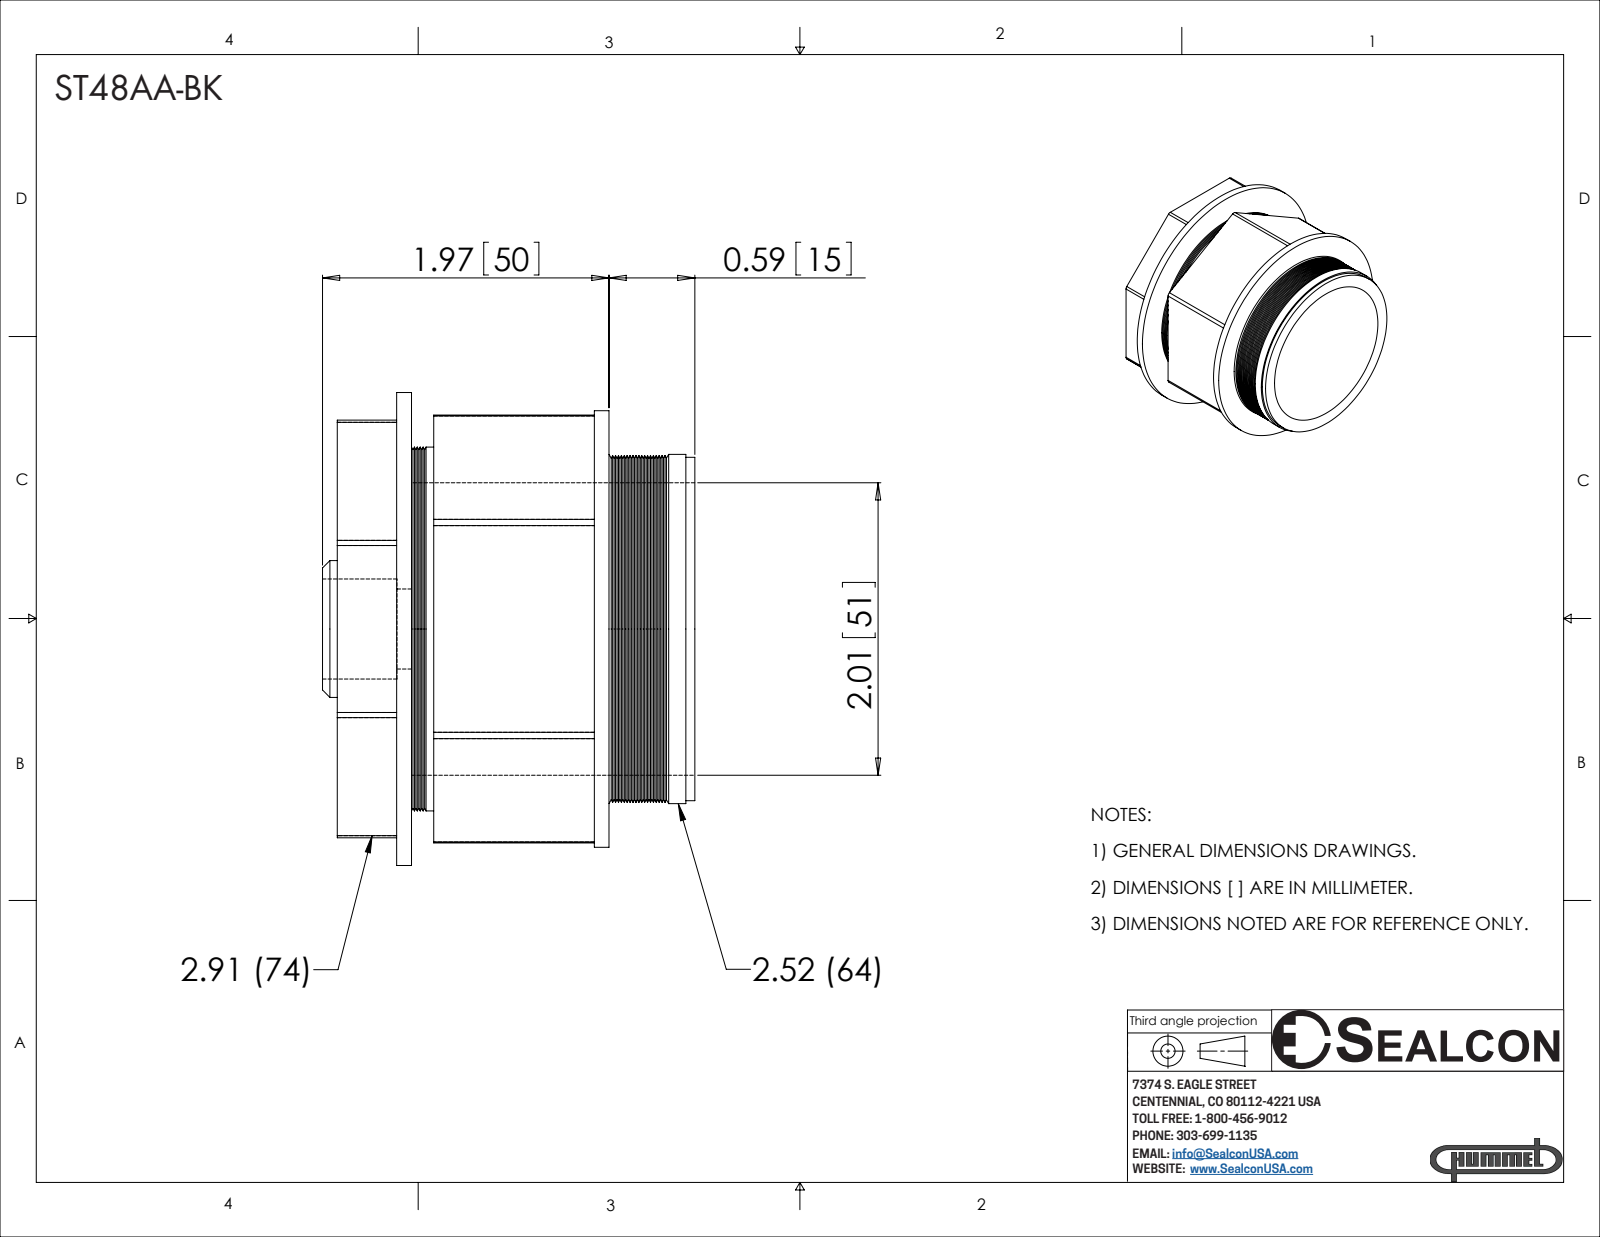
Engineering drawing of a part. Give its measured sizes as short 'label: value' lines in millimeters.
name: ST48AA-BK
written by: SolidWorks 2008 (CONFIG_CONTROL_DESIGN)
unit: mm
bodies: 2 solids, 156 faces (24 planar, 28 cylindrical, 104 other)
size: 82.6 × 82.6 × 61
volume: 114 300 mm³; area: 37 060 mm²
holes: 1× ⌀14, 1× ⌀17.4, 1× ⌀51.6
bosses: 1× ⌀82.6, 1× ⌀63.5, 1× ⌀59.9, 1× ⌀23.9
rounds: 14× R1.3
face distances: 13, 65, 2.6, 10.4, 43.4, 33, 30.4, 58.4, 48, 45.4
